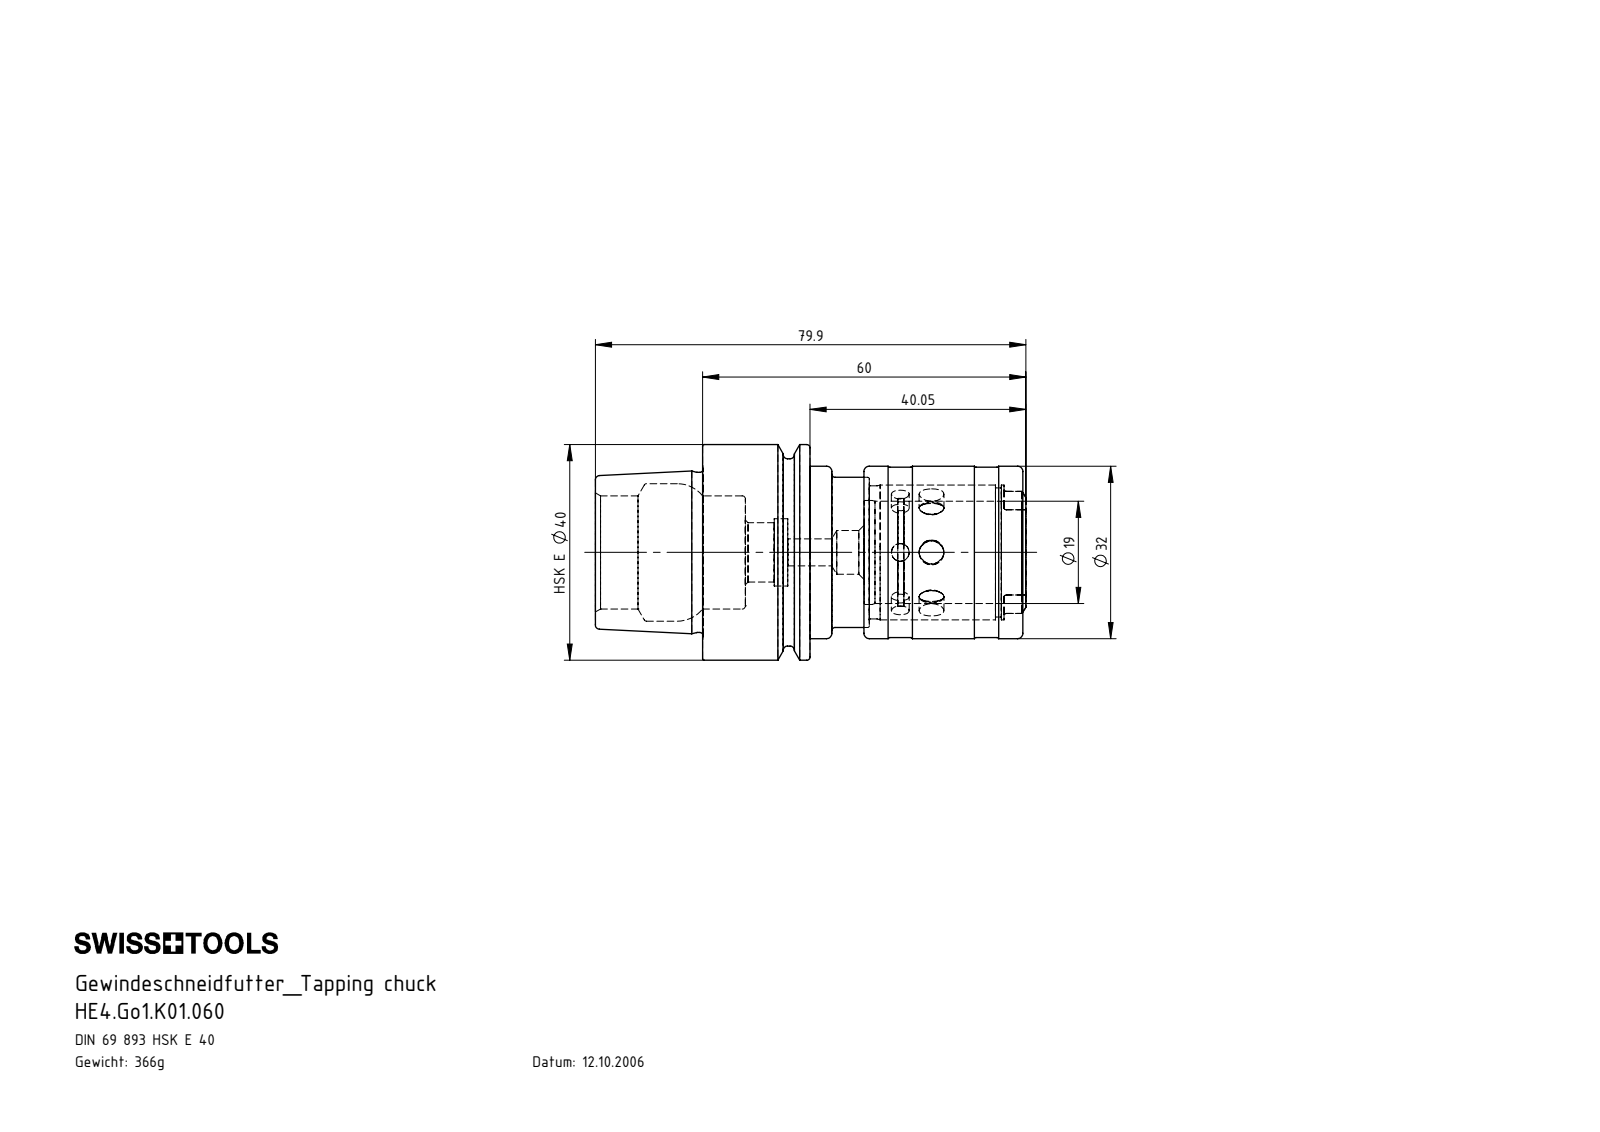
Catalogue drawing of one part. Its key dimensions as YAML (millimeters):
part_name: "HE4.Go1.K01.060; Einbausatz Go1_gespannt; Kugel Go1; Hülse Go1 (+6 more)"
step_written_by: "SolidWorks 2011 (AUTOMOTIVE_DESIGN)"
units: millimeters
bodies: {solids: 10, faces: 296, planar: 51, cylindrical: 97, other: 148}
overall_size: [79.9, 40, 40]
volume: 46527
surface_area: 24448
round_holes:
  - {diameter: 3.3, count: 3}
  - {diameter: 4.6, count: 3}
  - {diameter: 2, count: 1}
  - {diameter: 5, count: 1}
  - {diameter: 8, count: 1}
  - {diameter: 8.1, count: 1}
  - {diameter: 11, count: 1}
  - {diameter: 12.5, count: 1}
  - {diameter: 19, count: 1}
  - {diameter: 19.3, count: 1}
  - {diameter: 20.05, count: 1}
  - {diameter: 21, count: 1}
round_bosses_or_shafts:
  - {diameter: 40, count: 1}
  - {diameter: 34.75, count: 1}
  - {diameter: 32, count: 1}
  - {diameter: 31.6, count: 1}
  - {diameter: 29.71, count: 1}
  - {diameter: 27.85, count: 1}
  - {diameter: 25, count: 1}
  - {diameter: 24.7, count: 1}
partial_cylinders:
  - {radius: 2.15, count: 3}
  - {radius: 0.5, count: 2}
face_to_face_distances: [7.95, 30.95, 19.95, 10.05, 10.95, 22.05, 30, 38.9, 18.95, 11]
hole_center_spacings: [5.8]
